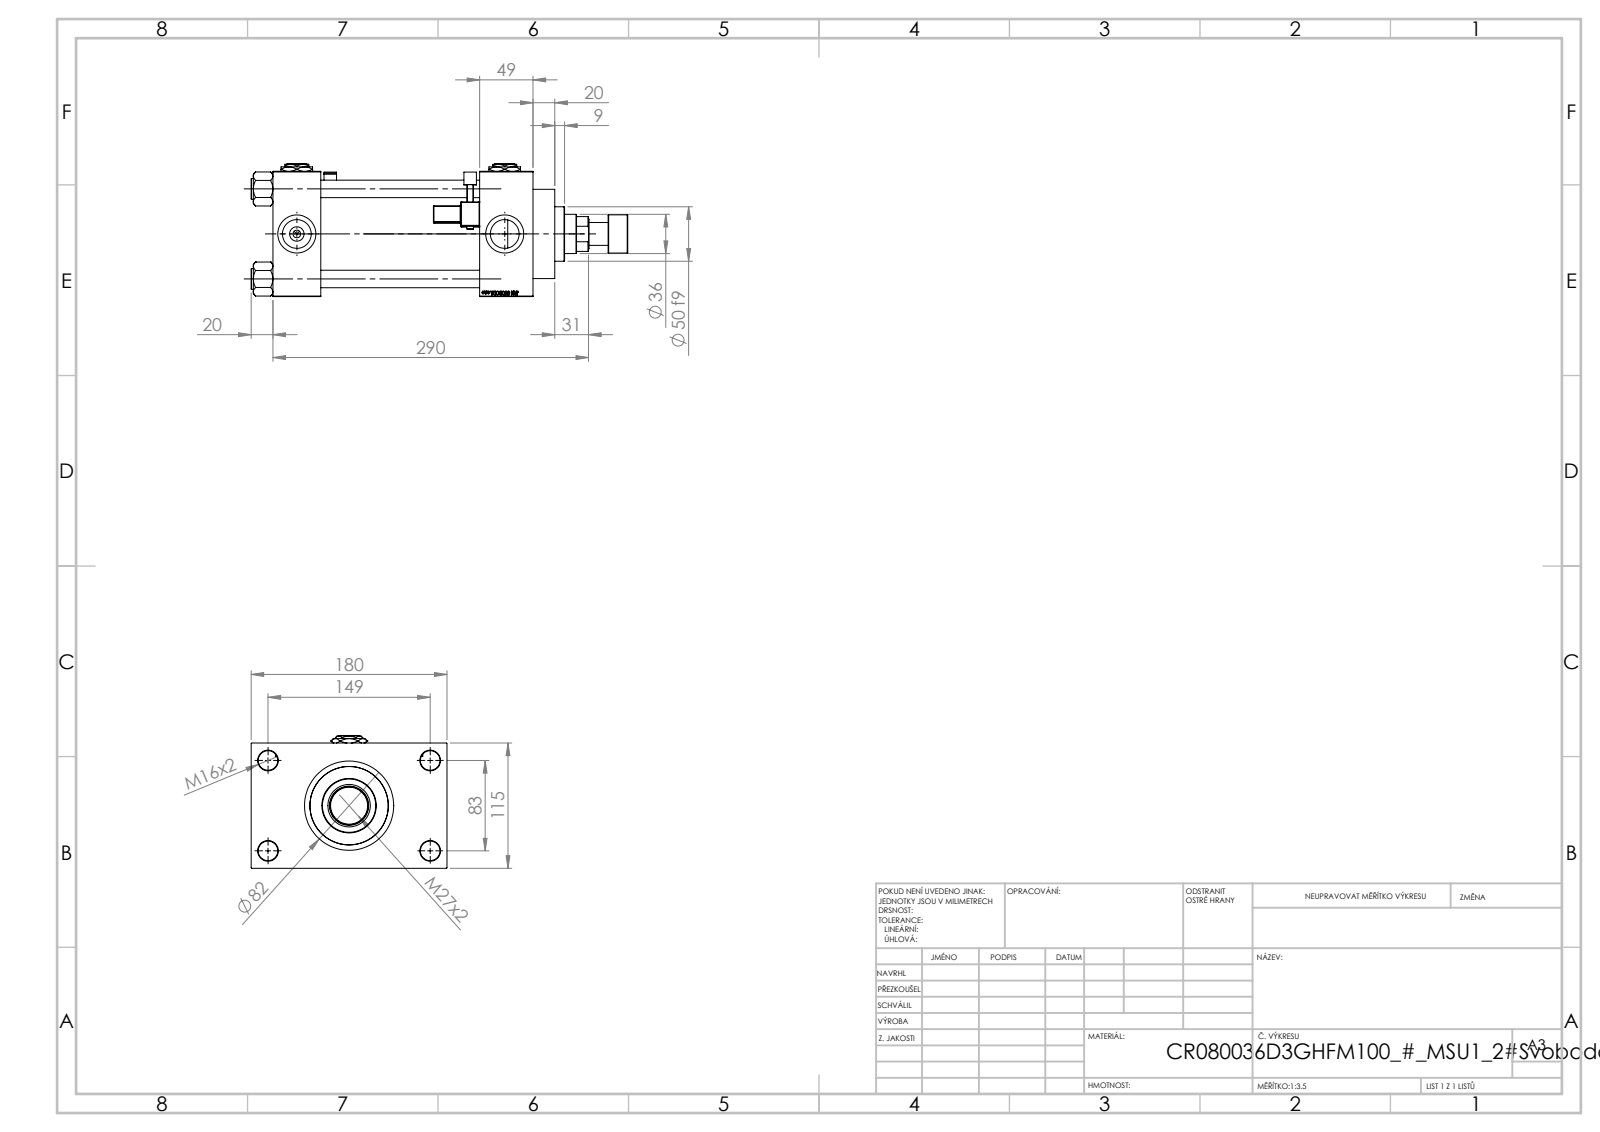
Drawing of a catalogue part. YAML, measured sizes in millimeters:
part_name: "V215_VC_A; V215CR_D_Body; V215CR_MSU; V215CR_VCP_D (+4 more)"
step_written_by: "SolidWorks 2019 (CONFIG_CONTROL_DESIGN)"
units: millimeters
bodies: {solids: 16, faces: 1420, planar: 655, cylindrical: 163, other: 602}
overall_size: [346, 180, 122]
volume: 2239000
surface_area: 388177
round_holes:
  - {diameter: 16, count: 4}
  - {diameter: 18, count: 4}
  - {diameter: 26.44, count: 4}
  - {diameter: 35, count: 4}
  - {diameter: 7, count: 3}
  - {diameter: 25.5, count: 1}
  - {diameter: 36, count: 1}
  - {diameter: 39, count: 1}
  - {diameter: 61, count: 1}
  - {diameter: 72, count: 1}
  - {diameter: 80, count: 1}
round_bosses_or_shafts:
  - {diameter: 19, count: 4}
  - {diameter: 6, count: 2}
  - {diameter: 86, count: 1}
  - {diameter: 82, count: 1}
  - {diameter: 50, count: 1}
  - {diameter: 35, count: 1}
  - {diameter: 21, count: 1}
partial_cylinders:
  - {radius: 0.5, count: 48}
  - {radius: 1, count: 2}
  - {radius: 2.5, count: 2}
  - {radius: 4, count: 2}
face_to_face_distances: [115, 146, 49, 195, 44, 190, 239, 32.5, 147.5, 100]
hole_center_spacings: [33.15, 58.48, 82.7, 85.28, 89.24, 115.85, 142.43, 83]
